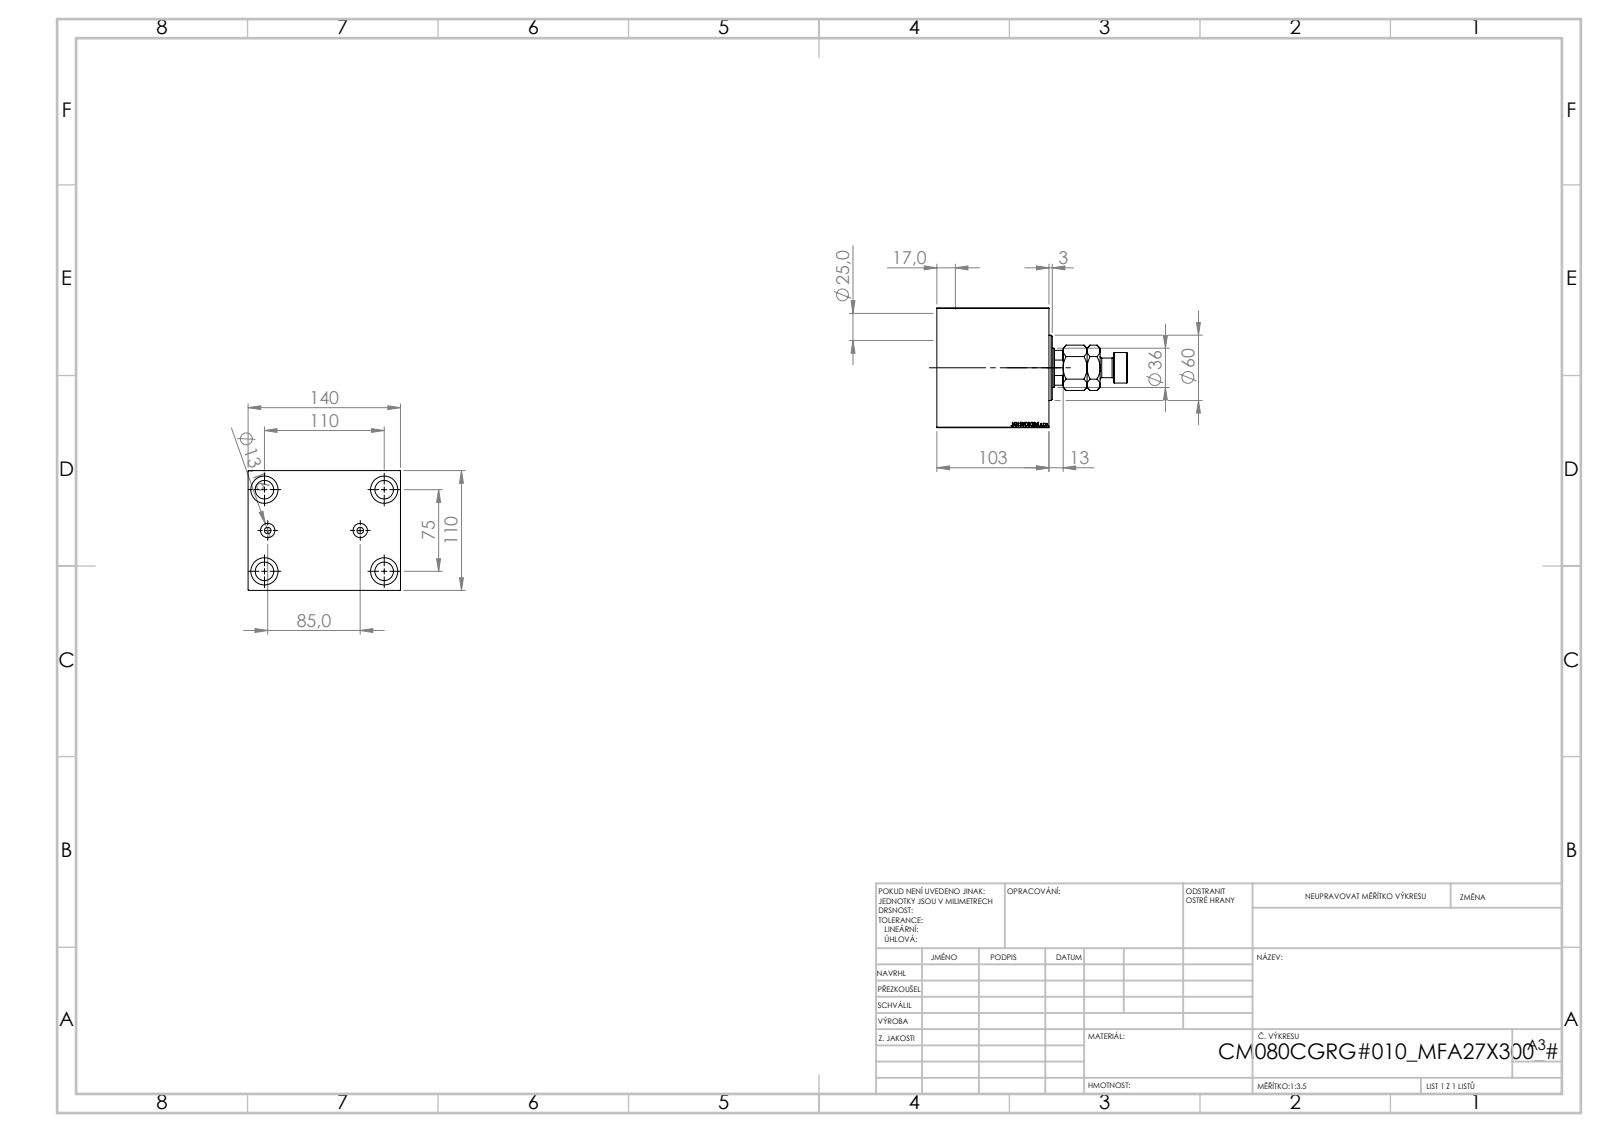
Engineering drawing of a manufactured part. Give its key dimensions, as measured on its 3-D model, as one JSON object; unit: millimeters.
{"part_name": "MFA; V450CM_C_VCP; V450CM_C_Body; V450CM_VC_B", "step_written_by": "SolidWorks 2019 (CONFIG_CONTROL_DESIGN)", "units": "millimeters", "bodies": {"solids": 4, "faces": 915, "planar": 427, "cylindrical": 62, "other": 426}, "overall_size": [176, 140, 110], "volume_mm3": 1458000, "surface_area_mm2": 168288, "round_holes": [[17, 4], [25, 4], [6, 2], [13.16, 2], [25.5, 1], [36, 1], [39.5, 1], [80, 1], [82, 1], [87, 1]], "round_bosses_or_shafts": [[60, 1], [28, 1], [18, 1]], "partial_cylinders_radius": [[17.5, 1]], "face_to_face_distances": [110, 140, 103, 48.25, 54.75, 10, 93, 20, 83, 38.25], "hole_center_spacings": [39.53, 66.57, 104.46, 42.5, 75, 110, 133.14, 85]}
